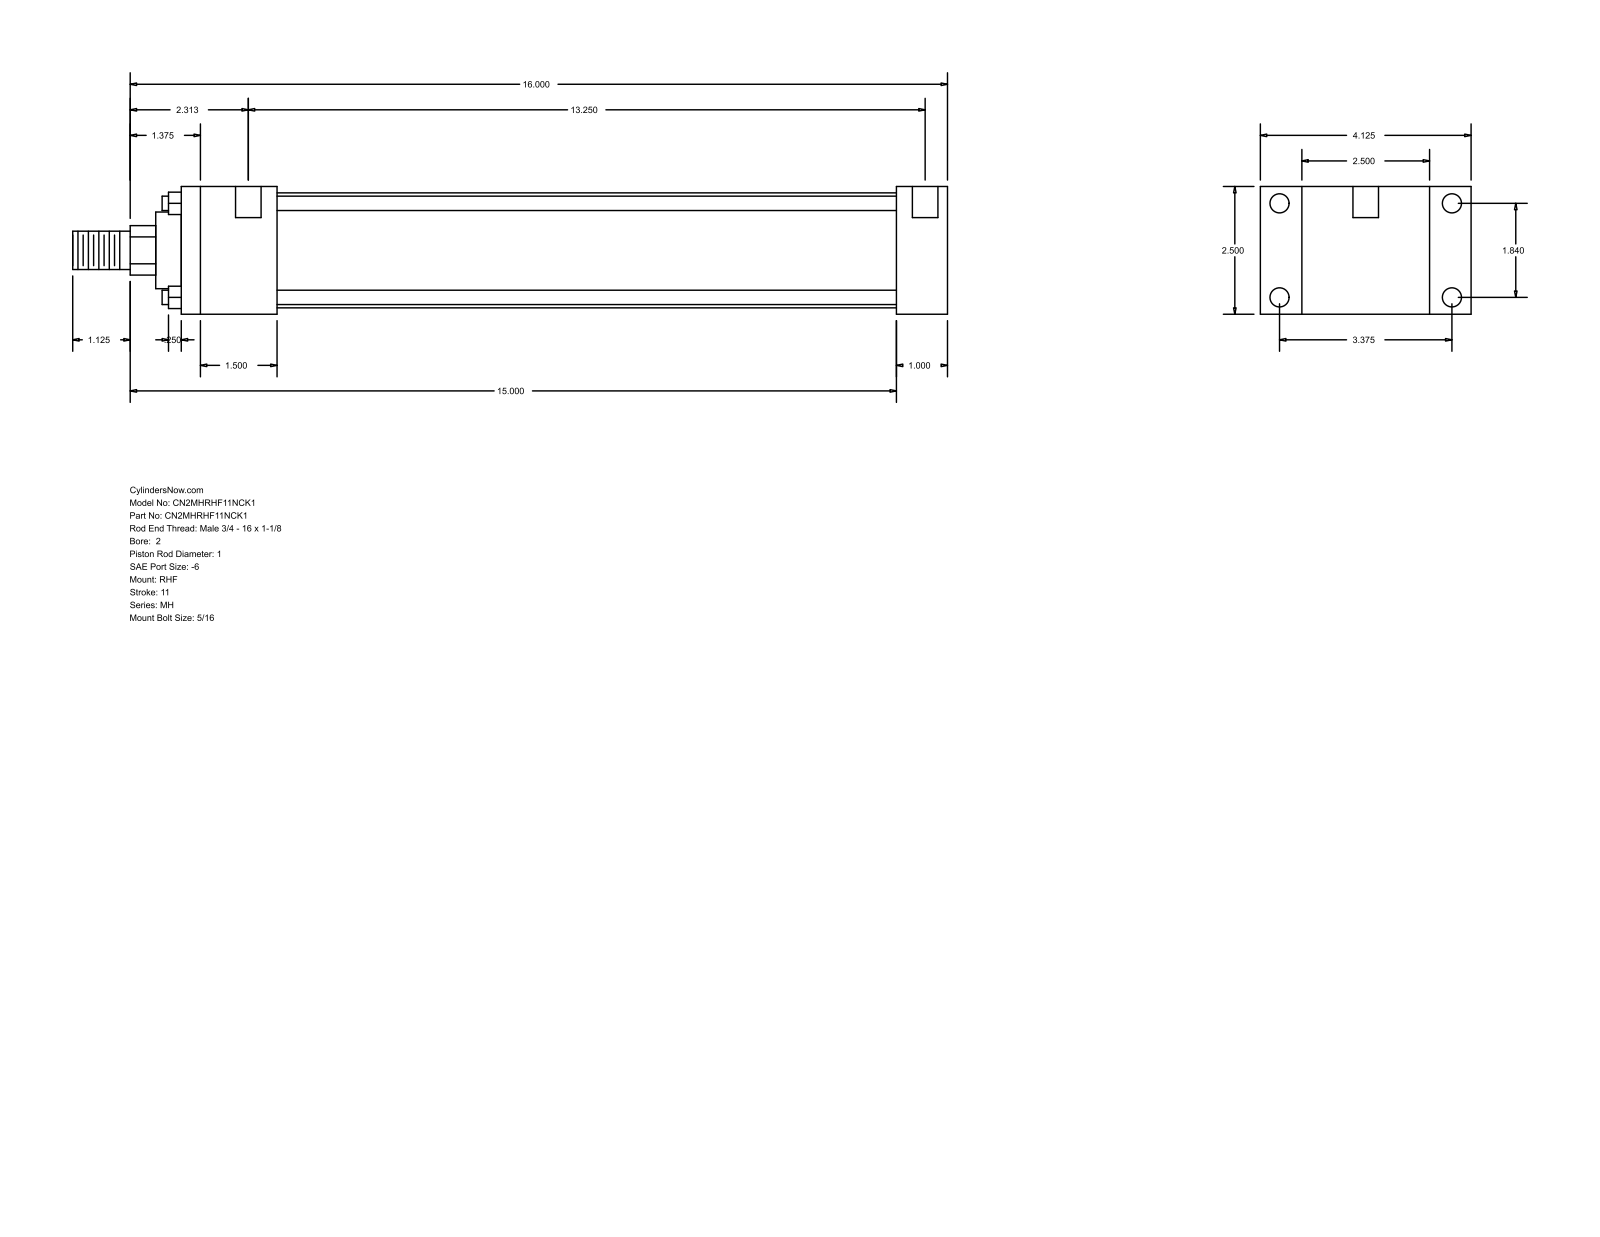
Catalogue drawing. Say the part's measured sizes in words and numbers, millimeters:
The part is named "MH_RHF__0200_1". Its 3-D file was written by "GSSL Pune (CONFIG_CONTROL_DESIGN)". It is 0 solids with 88 faces: 60 planar, 28 cylindrical and 0 other. Overall it measures 434.98 by 104.78 by 63.5 millimeters. Round holes: 4 of diameter 5.56, 4 of diameter 9.53, 2 of diameter 12.7. Round bosses or shafts: 4 of diameter 7.14, 1 of diameter 57.15, 1 of diameter 38.1, 1 of diameter 25.4, 1 of diameter 19.05. Partial cylindrical surfaces (rounded edges, fillets, slot ends): 1 of radius 12.29. The main face-to-face distances are 63.5, 25.4, 20.64, 84.14, 381, 355.6, 104.78, 47.63, 307.97, 333.37. The hole center spacings are 46.74, 85.72, 97.63, 344.48, 3.17, 4.76, 336.55, 339.72.
